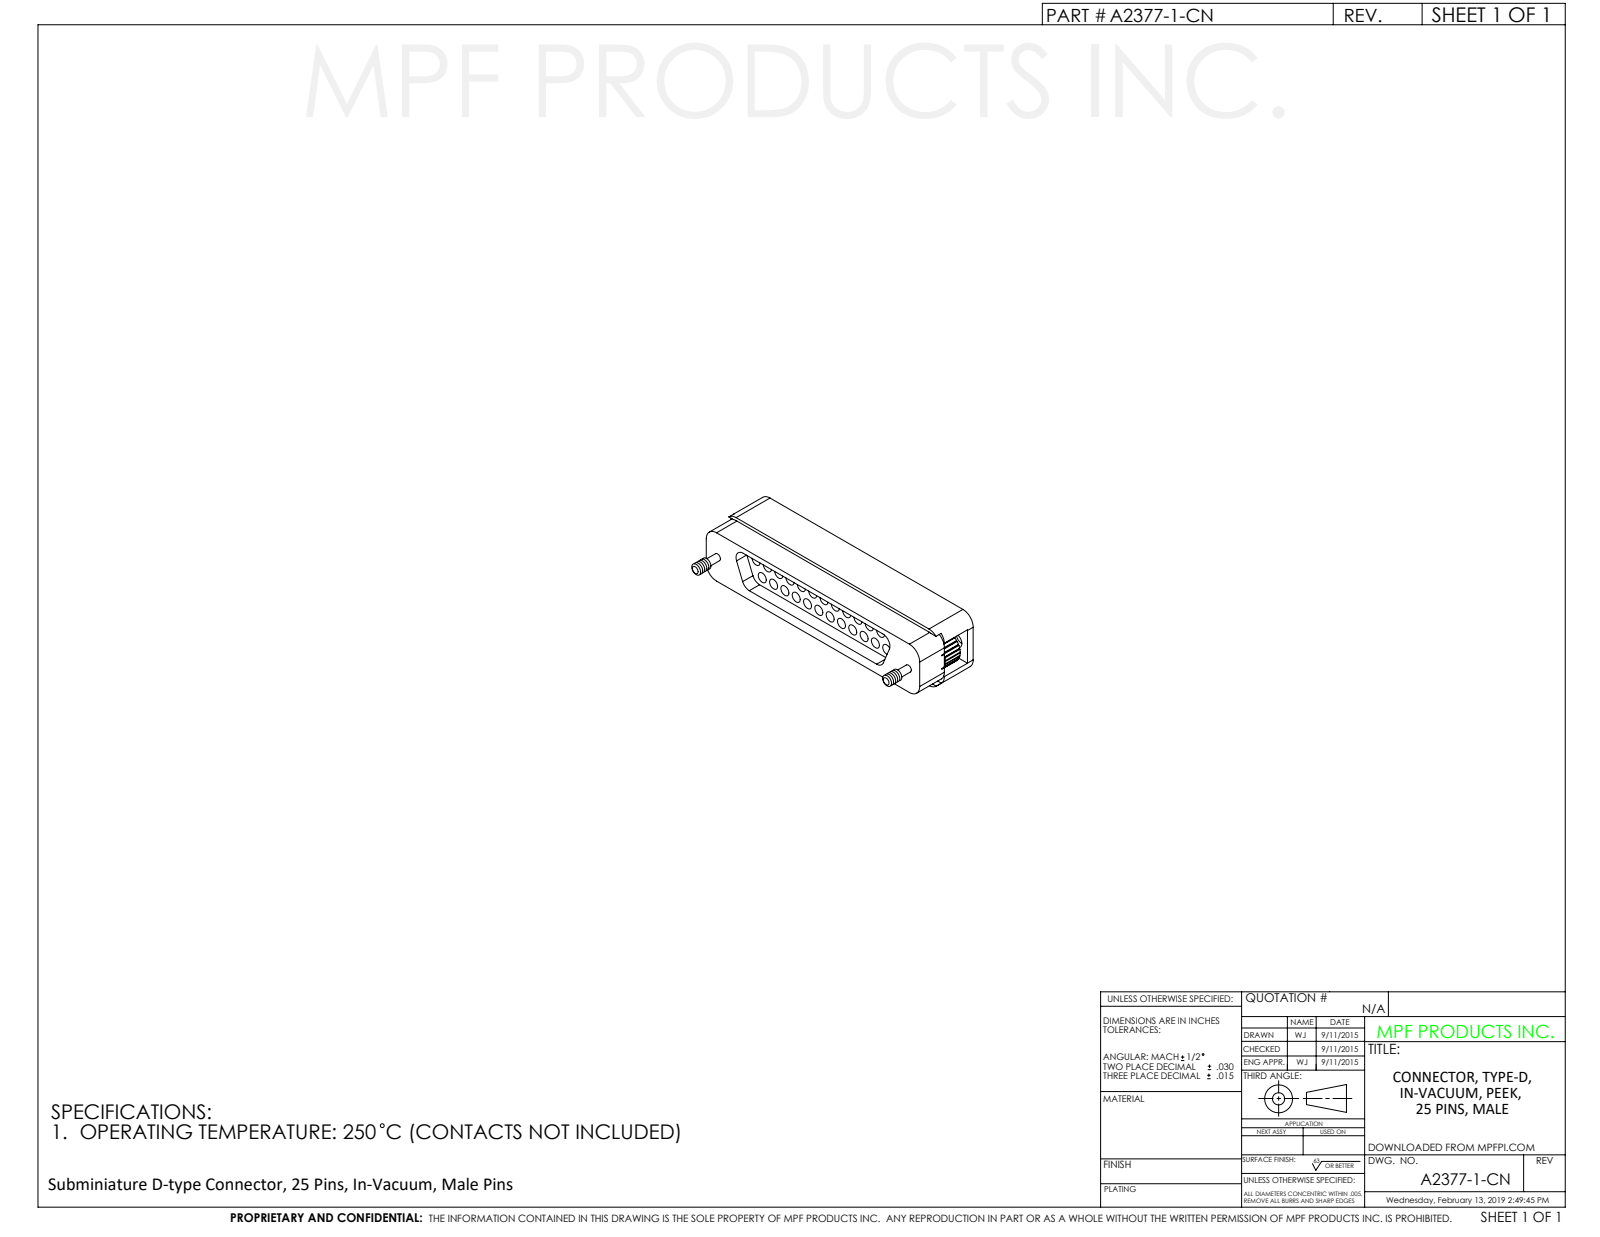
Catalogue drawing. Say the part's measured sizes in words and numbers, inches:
The part is named "A2377-1-CN". Its 3-D file was written by "SolidWorks 2012 (CONFIG_CONTROL_DESIGN)". It is 3 solids with 503 faces: 270 planar, 185 cylindrical and 48 other. Overall it measures 2.093 by 0.737 by 0.475 inches. Its volume is 0.357 cubic inches and its surface area 8.814 square inches. Round holes: 25 of diameter 0.08, 13 of diameter 0.078, 12 of diameter 0.078, 2 of diameter 0.11, 2 of diameter 0.15. Round bosses or shafts: 2 of diameter 0.139, 2 of diameter 0.056. Partial cylindrical surfaces (rounded edges, fillets, slot ends): 8 of radius 0.1, 4 of radius 0.07, 4 of radius 0.075, 2 of radius 0.118. The main face-to-face distances are 0.475, 0.036, 0.439, 0.443, 0.407, 0.032, 0.52, 0.42, 0.1, 0.375. The hole center spacings are 0.22, 0.33, 0.11, 0.126, 0.55, 0.197, 0.11, 0.13.
